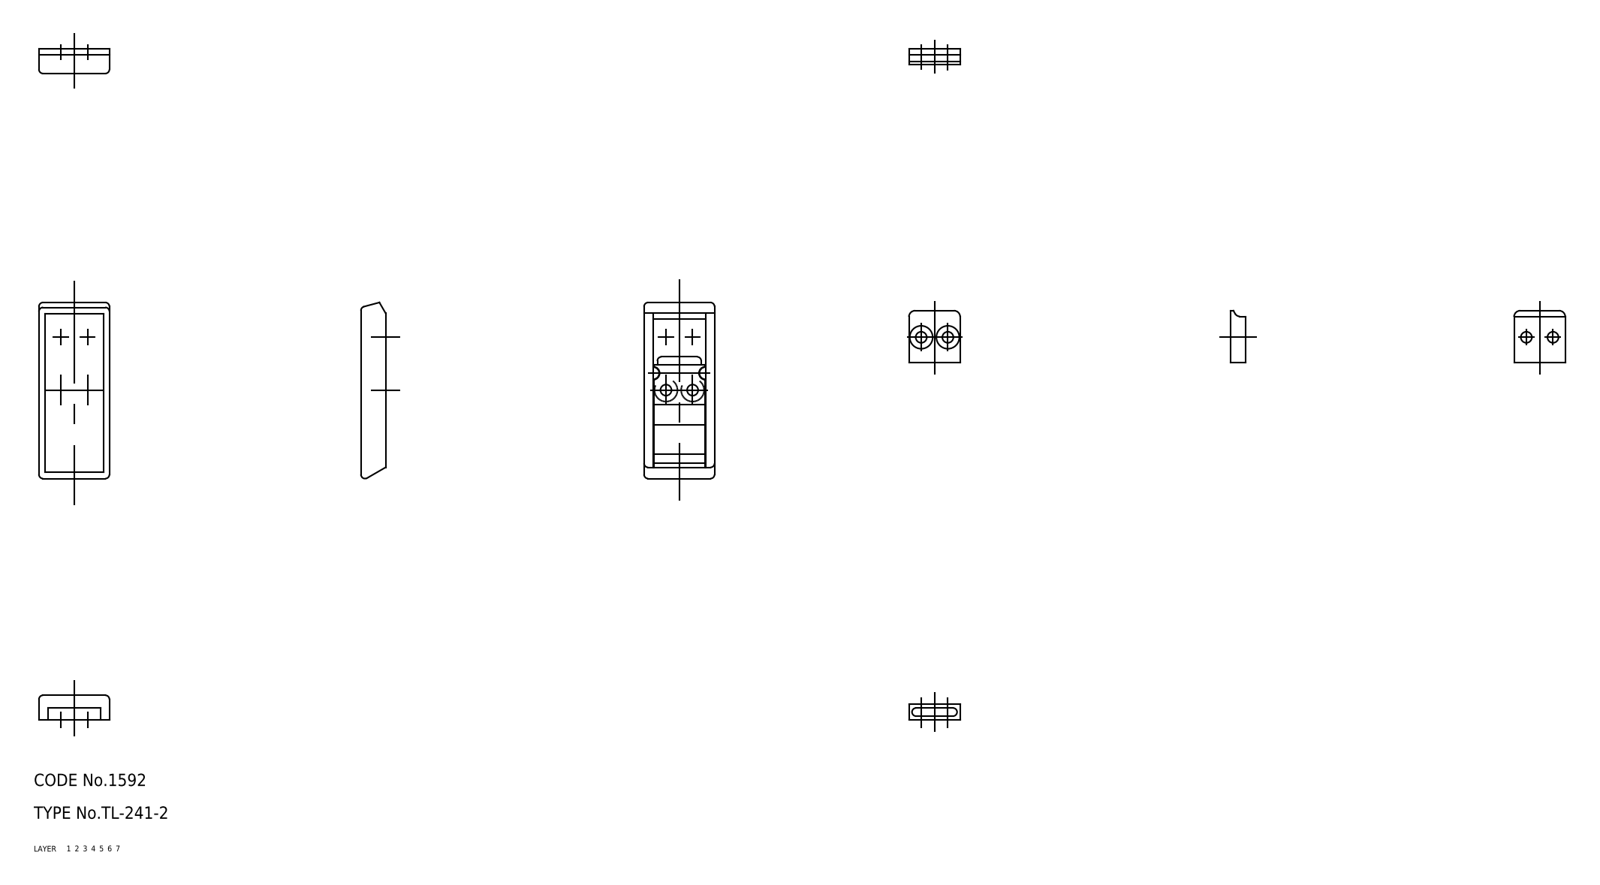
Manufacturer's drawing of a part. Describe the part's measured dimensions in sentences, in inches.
The part is named "keeper; TL_241_2_30991_36". Its 3-D file was written by "CADfix (AUTOMOTIVE_DESIGN)". It is 2 solids with 92 faces: 0 planar, 0 cylindrical and 92 other. Overall it measures 1.693 by 0.677 by 0.236 inches. Its volume is 0.228 cubic inches and its surface area 5.301 square inches.
